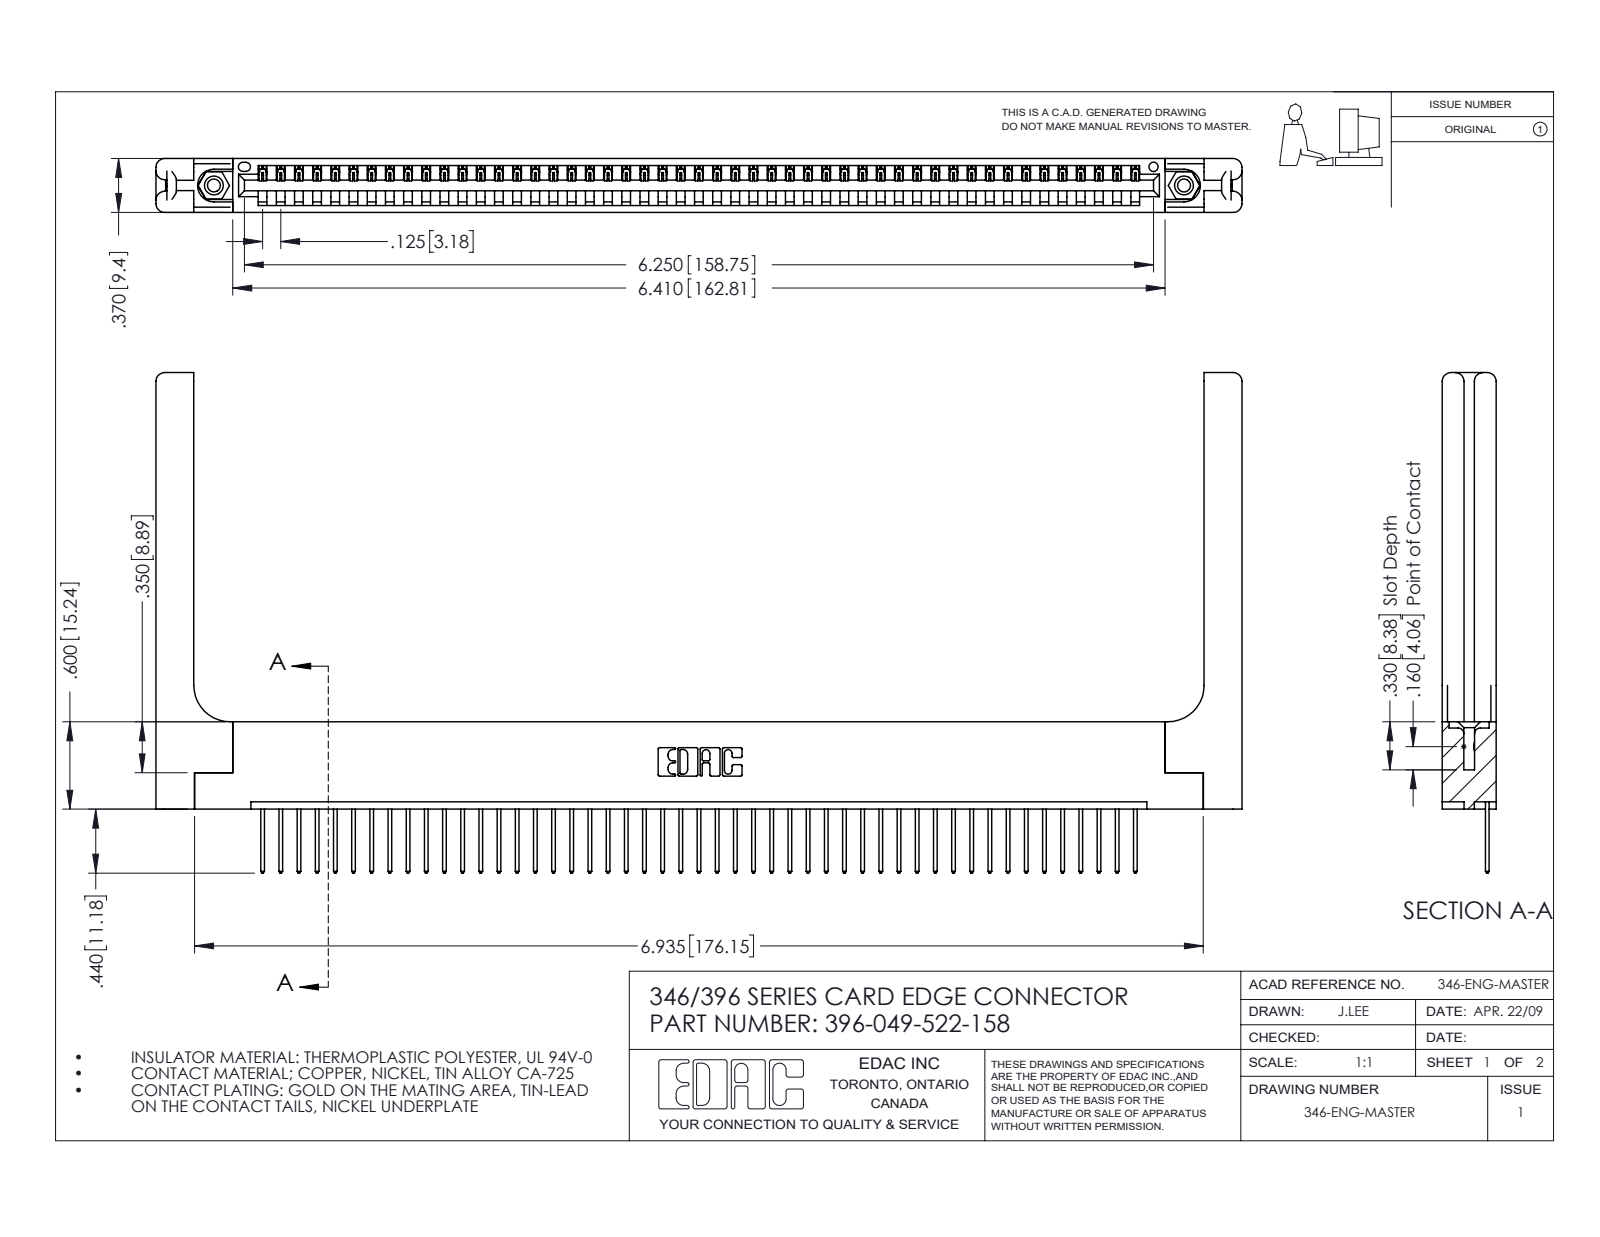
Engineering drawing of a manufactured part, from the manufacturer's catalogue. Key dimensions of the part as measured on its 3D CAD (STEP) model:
Part name (STEP PRODUCT): 345-292-001_345-293-122; 346 Part_Flush Mounting Lugs - 0.156 Dia-TH; 396-049-522-158; 346-220-058_345-220-058 (+1 more)
STEP written by: SolidWorks 2016 (CONFIG_CONTROL_DESIGN)
Units: inches
Bodies: 54 solids, 3220 faces (2184 planar, 976 cylindrical, 60 other)
Overall size (bounding box): 7.466 × 3.44 × 0.37
Volume: 1.57 in³ · Surface area: 43.68 in²
Round holes (diameter × count): ⌀0.089 ×2, ⌀0.125 ×2, ⌀0.156 ×2, ⌀0.064 ×1
Round bosses / shafts (diameter × count): ⌀0.155 ×2
Partial cylindrical surfaces — rounded edges, fillets, slot ends (radius × count): R0.006 ×98, R0.01 ×98, R0.01 ×22, R0.06 ×16, R0.007 ×6, R0.031 ×6, R0.026 ×3, R0.03 ×2
Main face-to-face distances: 0.37, 0.048, 0.322, 0.072, 0.148, 0.25, 0.15, 0.298, 0.025, 0.222
Hole centre spacings: 0.246, 6.461, 6.67
